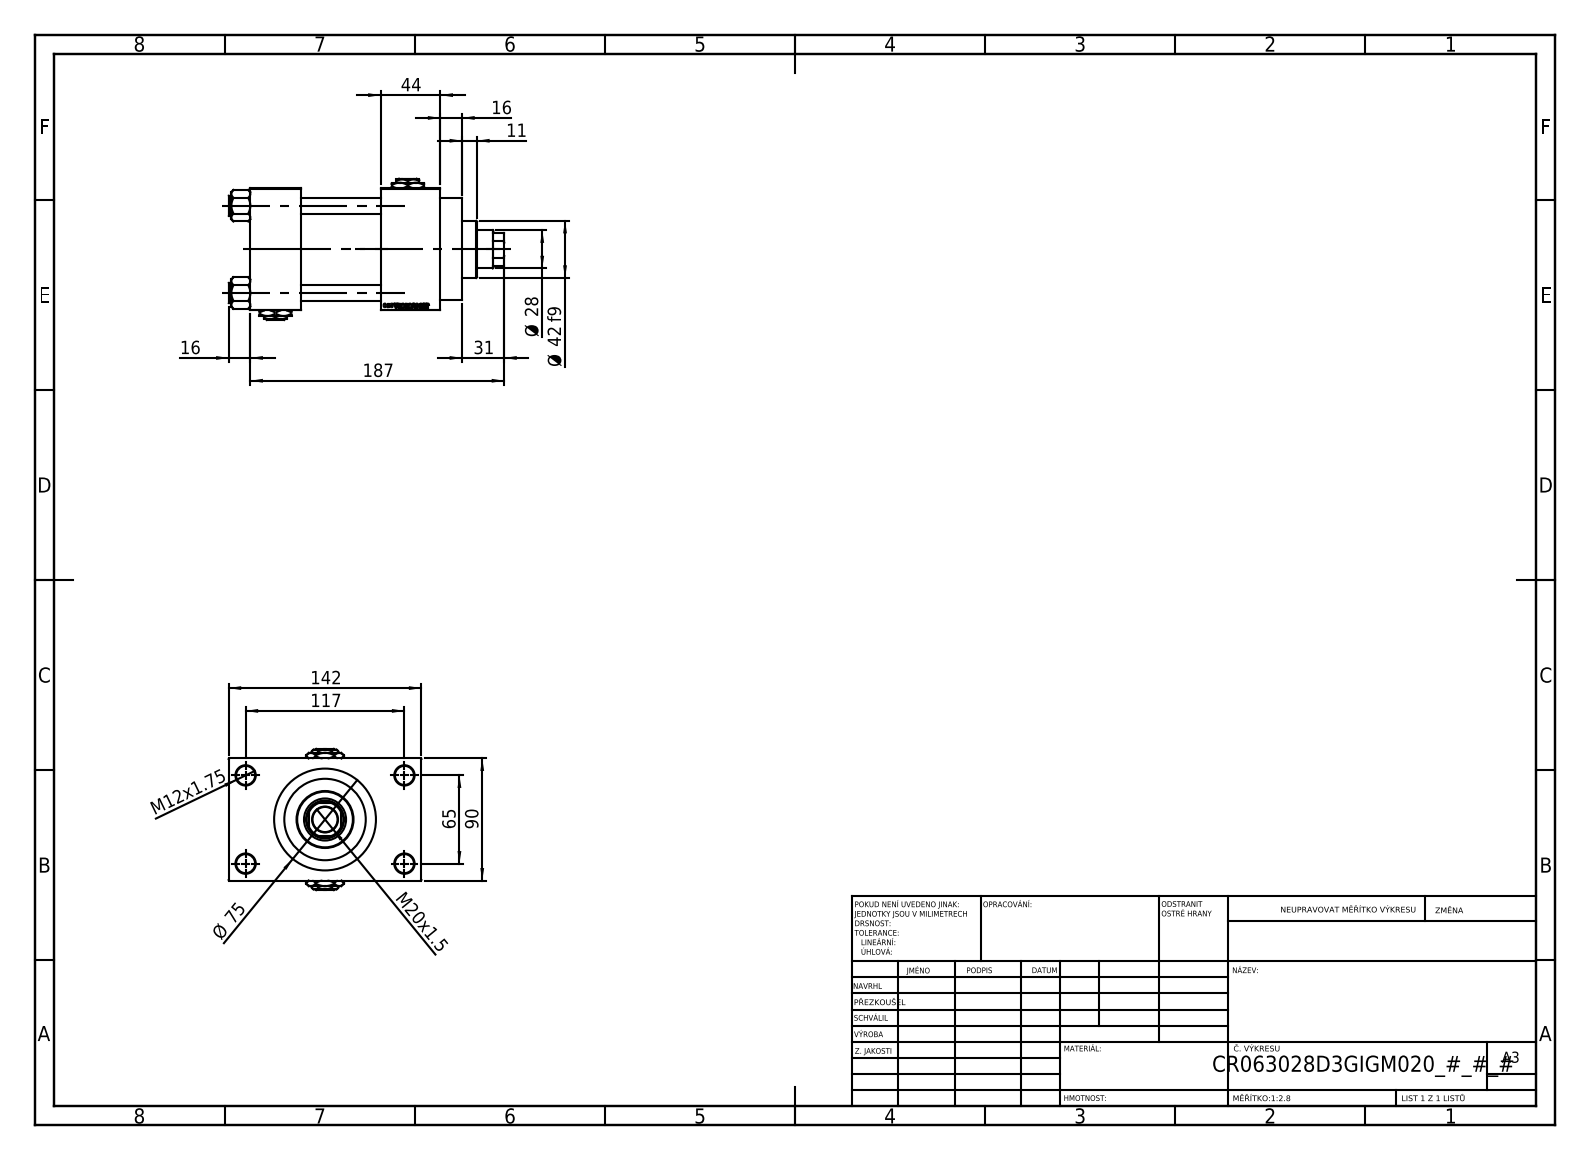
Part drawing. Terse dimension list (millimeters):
name: Zatka_pro_OIL_PORT; NUT_M5_D; V215CR_D_TYCINKA; V215CR_VCP_D (+2 more)
written by: SolidWorks 2019 (CONFIG_CONTROL_DESIGN)
unit: mm
bodies: 13 solids, 1198 faces (543 planar, 95 cylindrical, 560 other)
size: 203 × 142 × 104
volume: 1 106 000 mm³; area: 202 723 mm²
holes: 4× ⌀12, 4× ⌀14, 3× ⌀7, 3× ⌀20.96, 3× ⌀30, 1× ⌀18.5, 1× ⌀28, 1× ⌀31, 1× ⌀50, 1× ⌀60, 1× ⌀63
bosses: 4× ⌀15, 1× ⌀75, 1× ⌀69, 1× ⌀42
rounds: 1× R13.5
face distances: 90, 59, 37, 96, 103, 140, 44, 26, 116, 142
hole spacings: 26.35, 45.47, 64.3, 66.92, 69.81, 90.65, 111.34, 65
